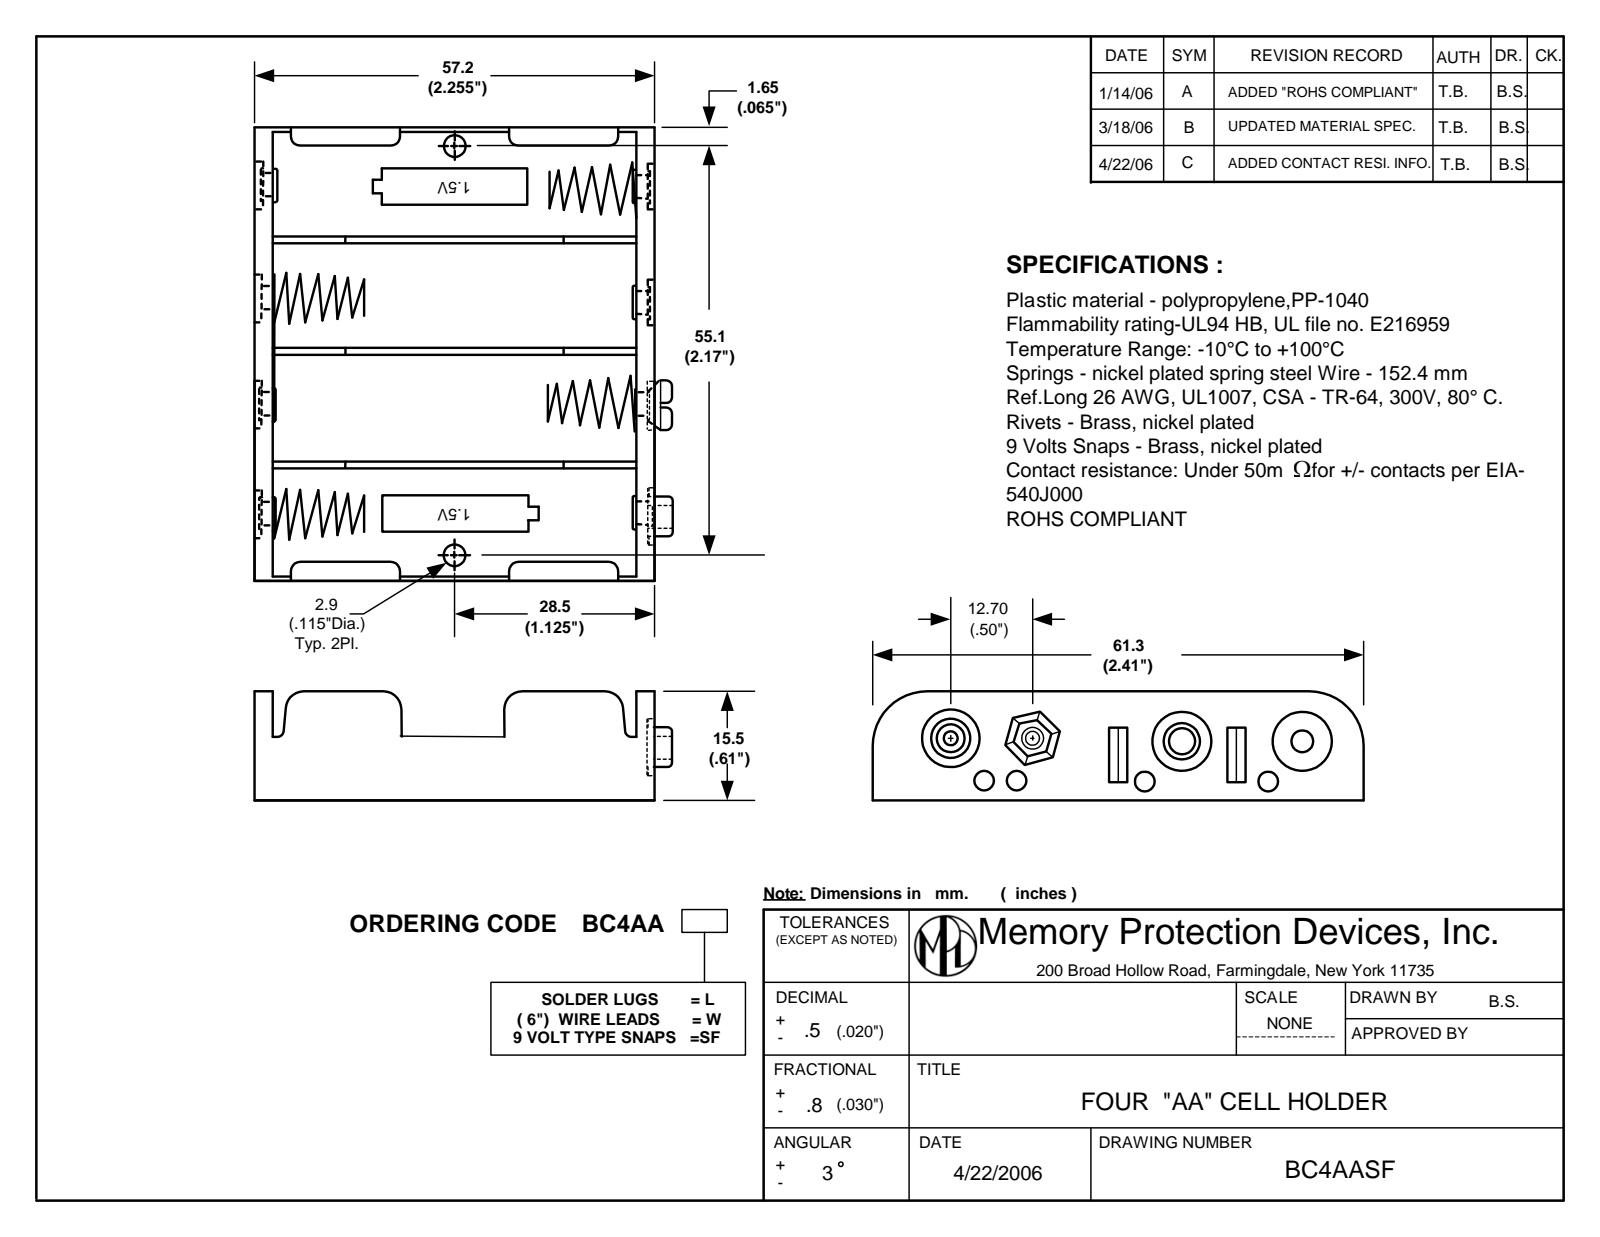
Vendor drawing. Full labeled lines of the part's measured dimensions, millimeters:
Part name (STEP PRODUCT): BC4AASF
STEP written by: SolidWorks 2016 (AUTOMOTIVE_DESIGN)
Units: millimetres
Bodies: 11 solids, 599 faces (294 planar, 209 cylindrical, 96 other)
Overall size (bounding box): 61.3 × 60.13 × 15.5
Volume: 10 325 mm³ · Surface area: 18 036 mm²
Round holes (diameter × count): ⌀3.7 ×8, ⌀1.8 ×4, ⌀2 ×4, ⌀2.3 ×4, ⌀3 ×4, ⌀7.4 ×4, ⌀2.9 ×2, ⌀2.2 ×1, ⌀2.86 ×1, ⌀4.95 ×1
Round bosses / shafts (diameter × count): ⌀4.7 ×8, ⌀6.2 ×4, ⌀3.5 ×4, ⌀0.7 ×2, ⌀0.6 ×2, ⌀7.92 ×1, ⌀5.71 ×1
Partial cylindrical surfaces — rounded edges, fillets, slot ends (radius × count): R2.5 ×8, R1.02 ×6, R1.98 ×2, R2.49 ×2, R3.5 ×2
Main face-to-face distances: 1.1, 1.55, 30.1, 55.7, 60.2, 29, 15.33, 30.65, 14.78, 15.32
Hole centre spacings: 30.65, 15.33, 38, 40.98, 48.82, 15.32, 7.8, 10.01
